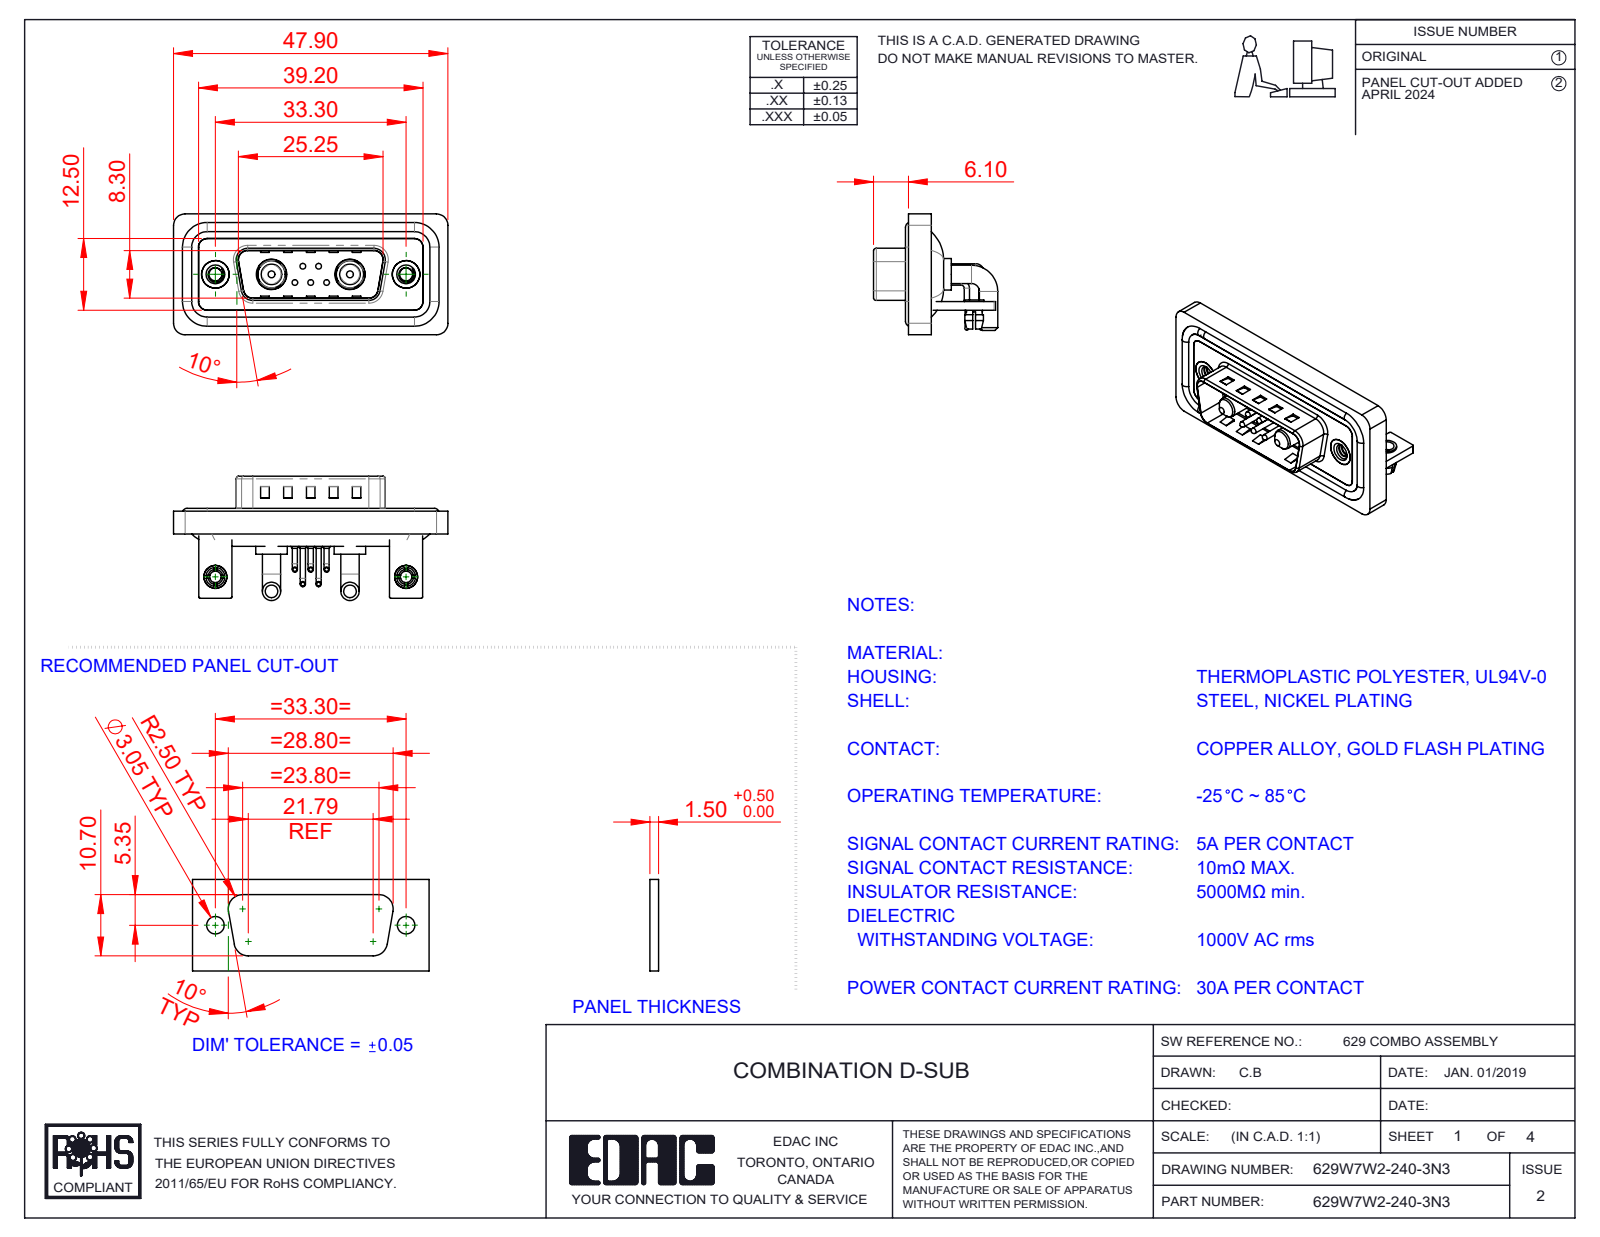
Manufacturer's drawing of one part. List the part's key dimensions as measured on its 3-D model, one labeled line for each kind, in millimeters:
Part name (STEP PRODUCT): 629Combo Contact Row 1; 629Combo Stabilizer Bracket; 629Combo Housing_7W2; 629Combo Board Lock (+7 more)
STEP written by: SolidWorks 2023 (CONFIG_CONTROL_DESIGN)
Units: millimetres
Bodies: 20 solids, 1215 faces (585 planar, 456 cylindrical, 174 other)
Overall size (bounding box): 47.9 × 21.7 × 21.1
Volume: 6 050 mm³ · Surface area: 9 975 mm²
Round holes (diameter × count): ⌀2 ×7, ⌀0.75 ×5, ⌀1.6 ×5, ⌀2.26 ×2, ⌀2.5 ×2, ⌀3.2 ×2, ⌀4 ×2, ⌀4.8 ×2, ⌀4.85 ×2, ⌀5 ×2, ⌀5.3 ×2
Round bosses / shafts (diameter × count): ⌀0.9 ×10, ⌀1.5 ×5, ⌀1 ×5, ⌀0.65 ×5, ⌀3.2 ×4, ⌀1.6 ×4, ⌀5.5 ×2, ⌀5.2 ×2
Partial cylindrical surfaces — rounded edges, fillets, slot ends (radius × count): R2 ×21, R1.5 ×18, R0.25 ×16, R0.5 ×9, R1.6 ×8, R1.01 ×5, R0.6 ×4, R0.65 ×4
Main face-to-face distances: 0.4, 1.5, 0.8, 2.9, 2.1, 1.1, 1.6, 1.2, 3.7, 4.5
Hole centre spacings: 3.16, 2.77, 9.8, 23.5, 33.3, 4.31, 4.33, 5.03
